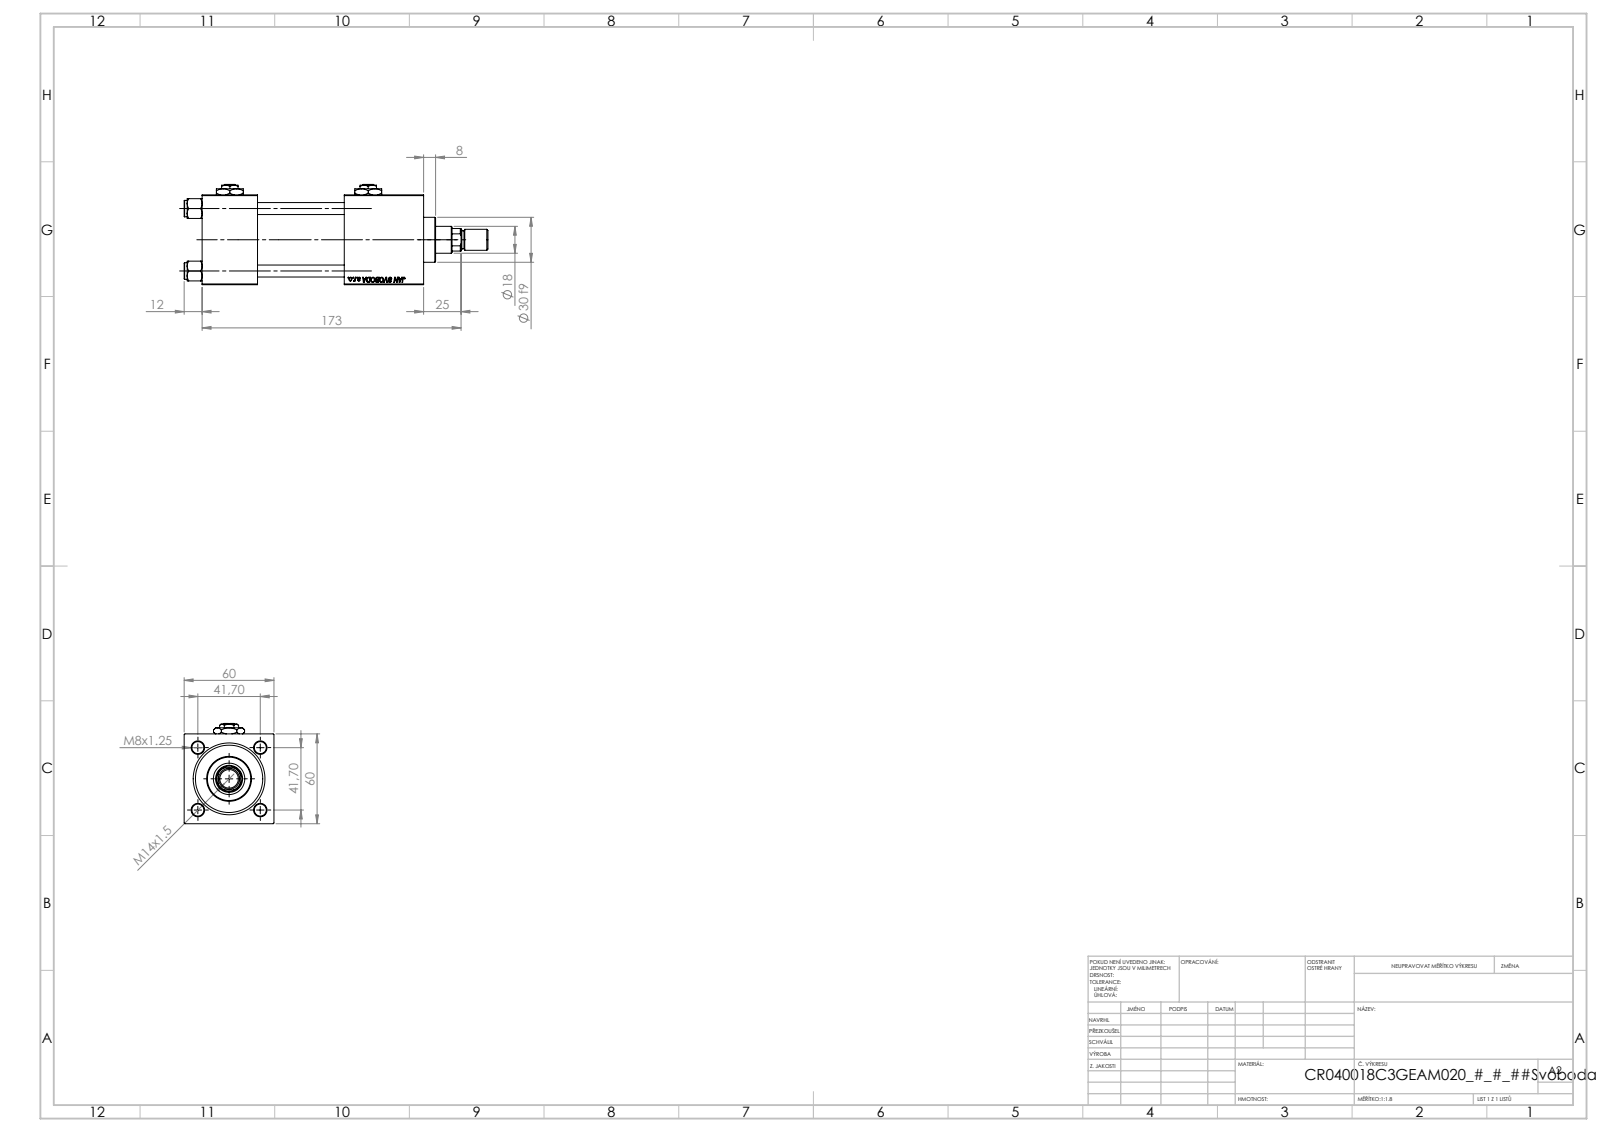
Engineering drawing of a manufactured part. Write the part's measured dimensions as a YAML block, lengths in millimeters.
part_name: "ROD_END_AH; NUT_M5_C; V215CR_C_TYCINKA; Zatka_pro_OIL_PORT (+3 more)"
step_written_by: "SolidWorks 2019 (CONFIG_CONTROL_DESIGN)"
units: millimeters
bodies: {solids: 14, faces: 1264, planar: 578, cylindrical: 102, other: 584}
overall_size: [203, 67, 60]
volume: 401513
surface_area: 109461
round_holes:
  - {diameter: 8, count: 4}
  - {diameter: 7, count: 2}
  - {diameter: 16.66, count: 2}
  - {diameter: 24, count: 2}
  - {diameter: 8.5, count: 1}
  - {diameter: 18, count: 1}
  - {diameter: 21, count: 1}
  - {diameter: 31, count: 1}
  - {diameter: 40, count: 1}
  - {diameter: 45, count: 1}
round_bosses_or_shafts:
  - {diameter: 11, count: 4}
  - {diameter: 46, count: 1}
  - {diameter: 30, count: 1}
  - {diameter: 14, count: 1}
  - {diameter: 12, count: 1}
partial_cylinders:
  - {radius: 8.5, count: 1}
face_to_face_distances: [60, 37, 53, 148, 111, 58, 95, 119.3, 82.3, 24.3]
hole_center_spacings: [29.49, 41.7, 58.97, 92.5]
